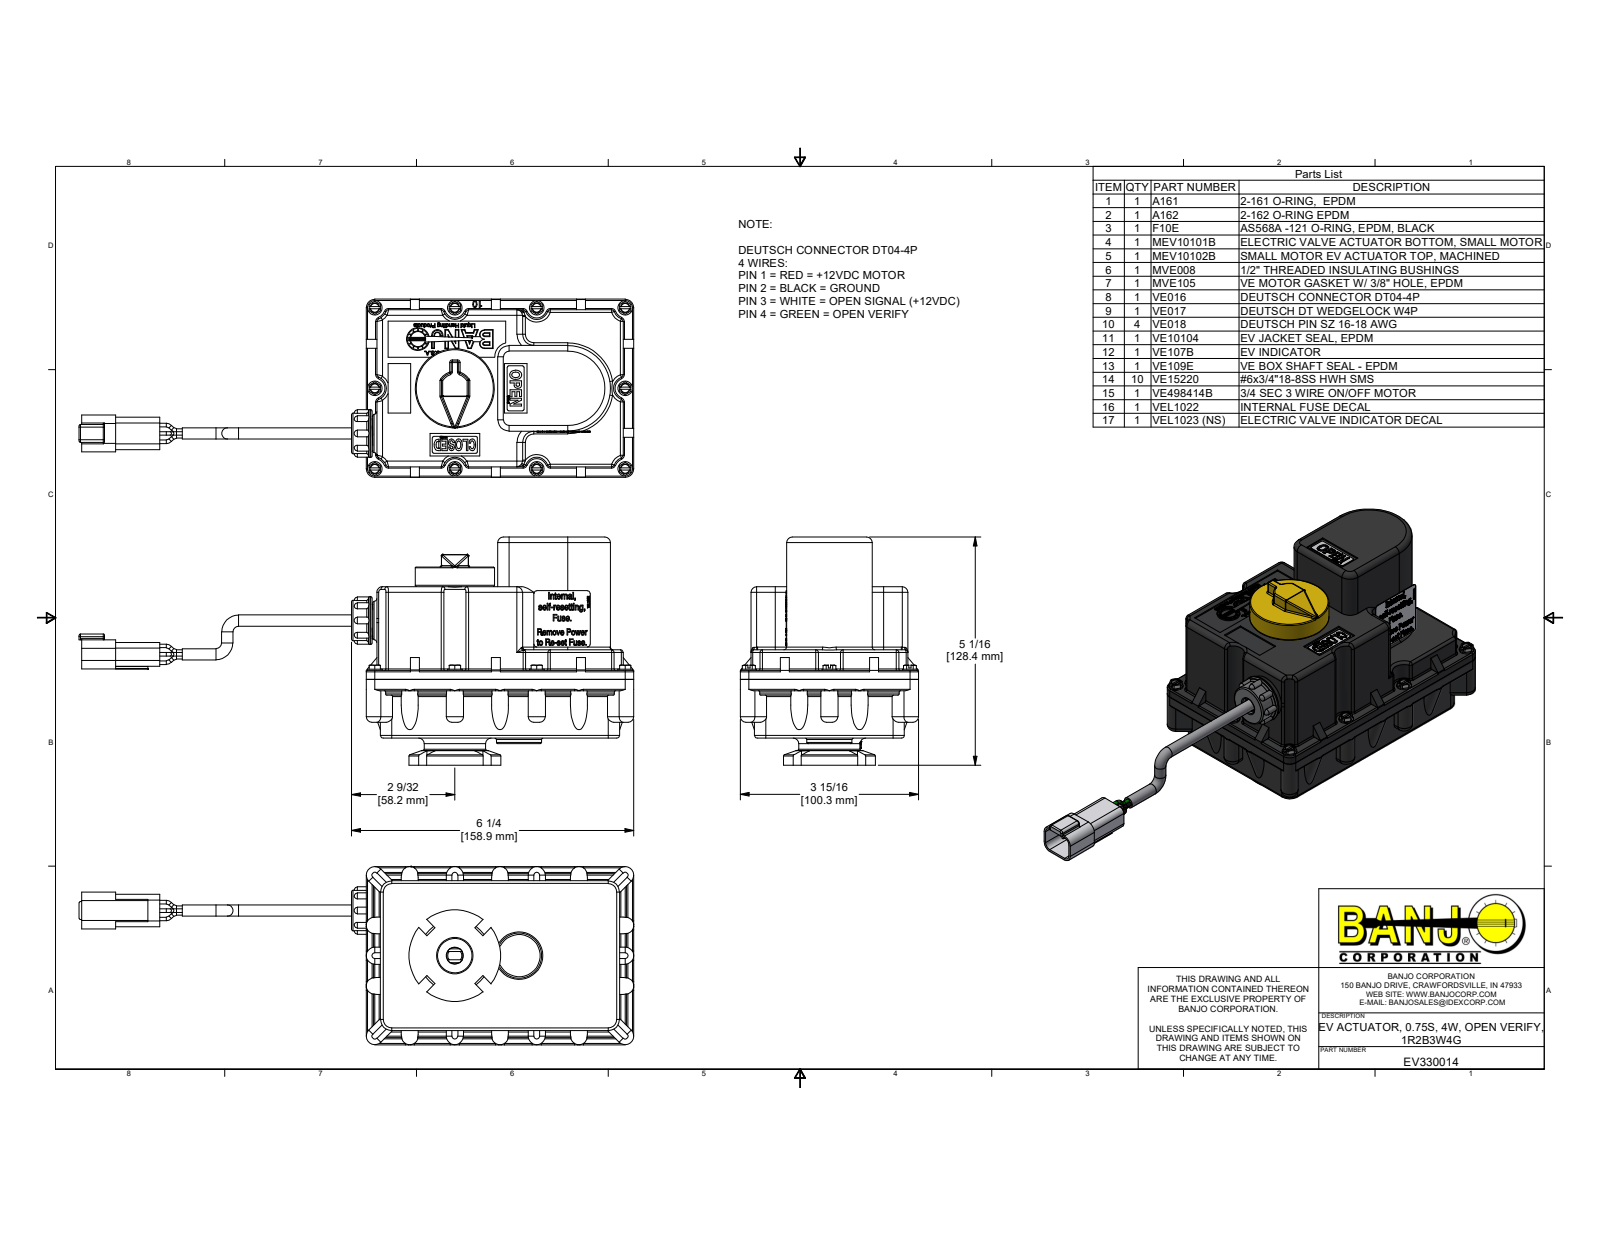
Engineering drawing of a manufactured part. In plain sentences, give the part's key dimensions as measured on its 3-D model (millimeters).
The part is named "EV330014; MEV10101B; MEV10102B; MEV10102BX (+8 more)". Its 3-D file was written by "Autodesk Inventor 2022 (AUTOMOTIVE_DESIGN)". It is 55 solids with 6111 faces: 2791 planar, 1317 cylindrical and 2003 other. Overall it measures 312.3 by 128.4 by 100.3 millimeters. Its volume is 592 200 cubic millimeters and its surface area 268 300 square millimeters. Round holes: 13 of diameter 3.8, 10 of diameter 2.8, 10 of diameter 4.1, 10 of diameter 5.1, 8 of diameter 1.3, 8 of diameter 2, 7 of diameter 2.1, 7 of diameter 2.4, 6 of diameter 1.2, 6 of diameter 3, 6 of diameter 4.5, 4 of diameter 0.8. Round bosses or shafts: 19 of diameter 2, 10 of diameter 8.3, 10 of diameter 3.5, 8 of diameter 2.6, 6 of diameter 6.4, 4 of diameter 8, 4 of diameter 3.3, 4 of diameter 2.6. Partial cylindrical surfaces (rounded edges, fillets, slot ends): 144 of radius 0.8, 70 of radius 0.5, 49 of radius 1.5, 43 of radius 0.9, 32 of radius 3.2, 24 of radius 8, 24 of radius 12.7, 16 of radius 9.9. The main face-to-face distances are 3.2, 85.2, 27.9, 5.1, 26, 33, 20.1, 65.2, 82, 1.9. The hole center spacings are 42.7, 52.3, 3.2, 5.5, 42.8, 45.3, 60.4, 3.2.
